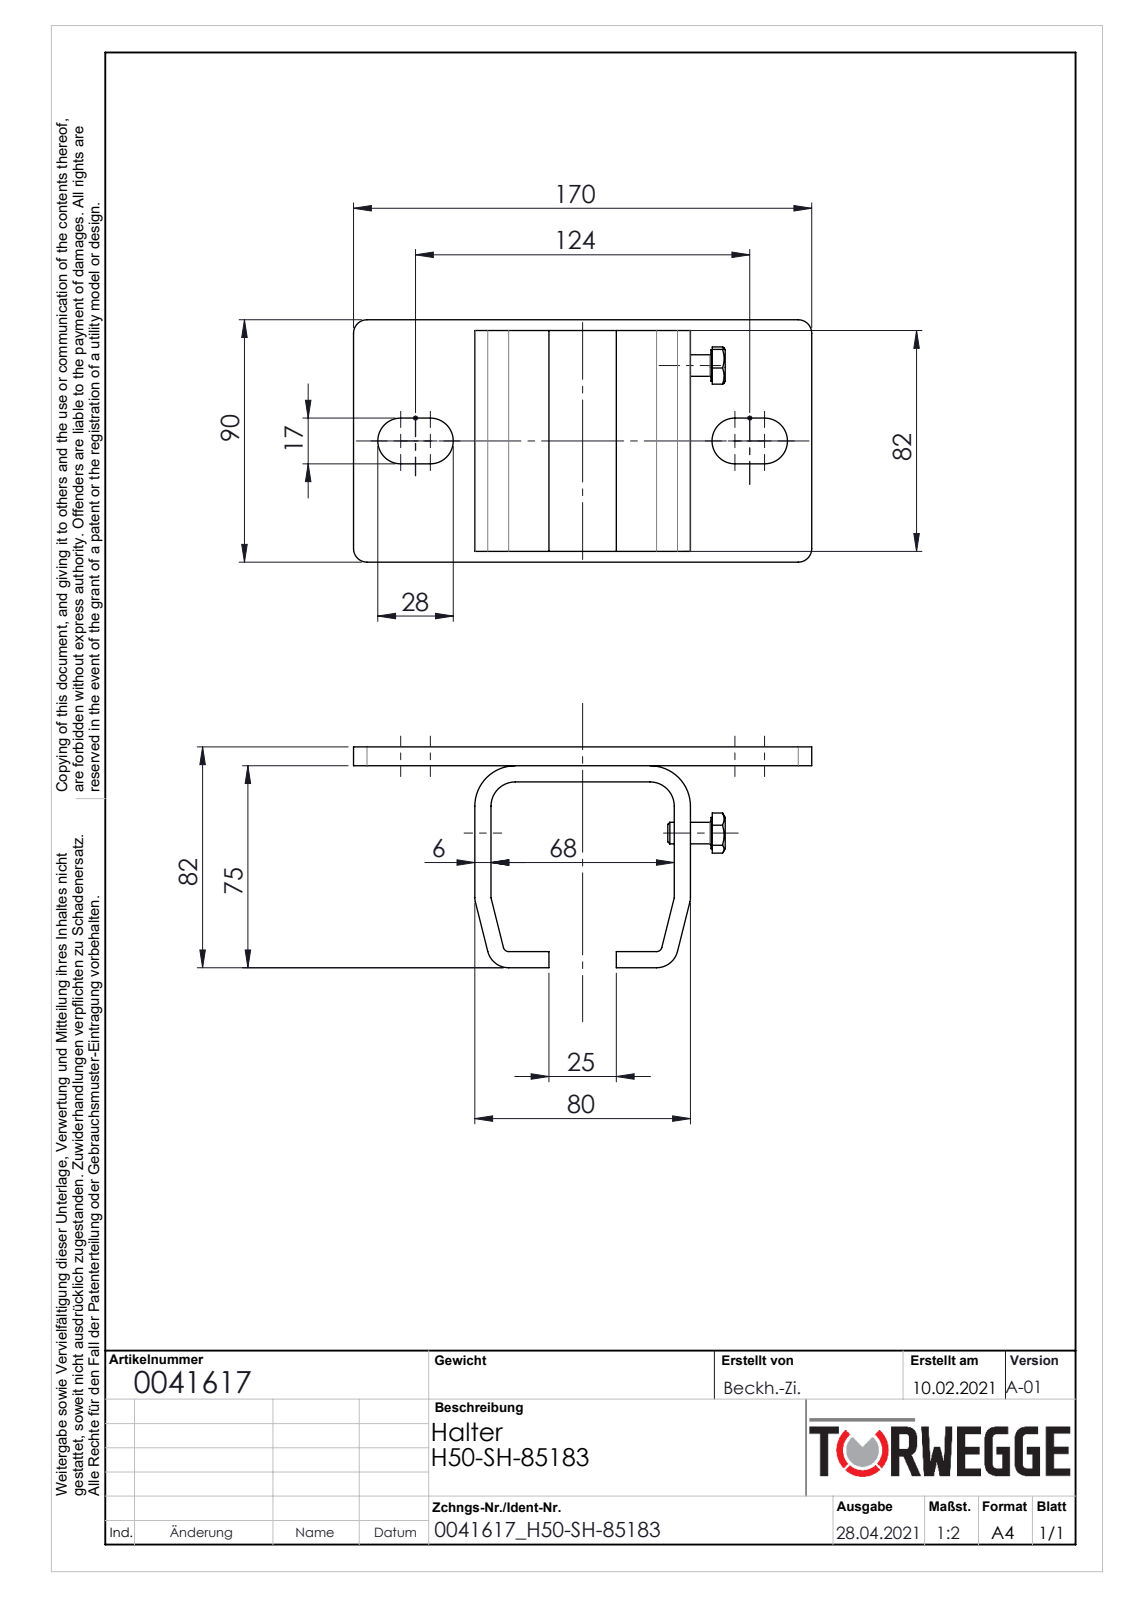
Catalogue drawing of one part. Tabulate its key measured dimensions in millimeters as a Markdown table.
| quantity | value |
| --- | --- |
| part name | 0041617 |
| STEP written by | SolidWorks 2020 (AUTOMOTIVE_DESIGN) |
| units | millimeters |
| bodies | 3 solids, 70 faces (38 planar, 26 cylindrical, 6 other) |
| overall size | 170 × 90 × 82 |
| volume | 219 557 mm³ |
| surface area | 77 485 mm² |
| round holes (diameter × count) | 6.8 × 1 |
| round bosses / shafts (diameter × count) | 11.6 × 1, 8 × 1 |
| partial cylindrical surfaces (radius × count) | 5 × 4, 8.5 × 4, 2 × 2, 6 × 2, 8 × 2, 9 × 2, 15 × 2 |
| main face-to-face distances | 6, 7, 74, 69, 13, 82, 68, 80, 63, 76 |
